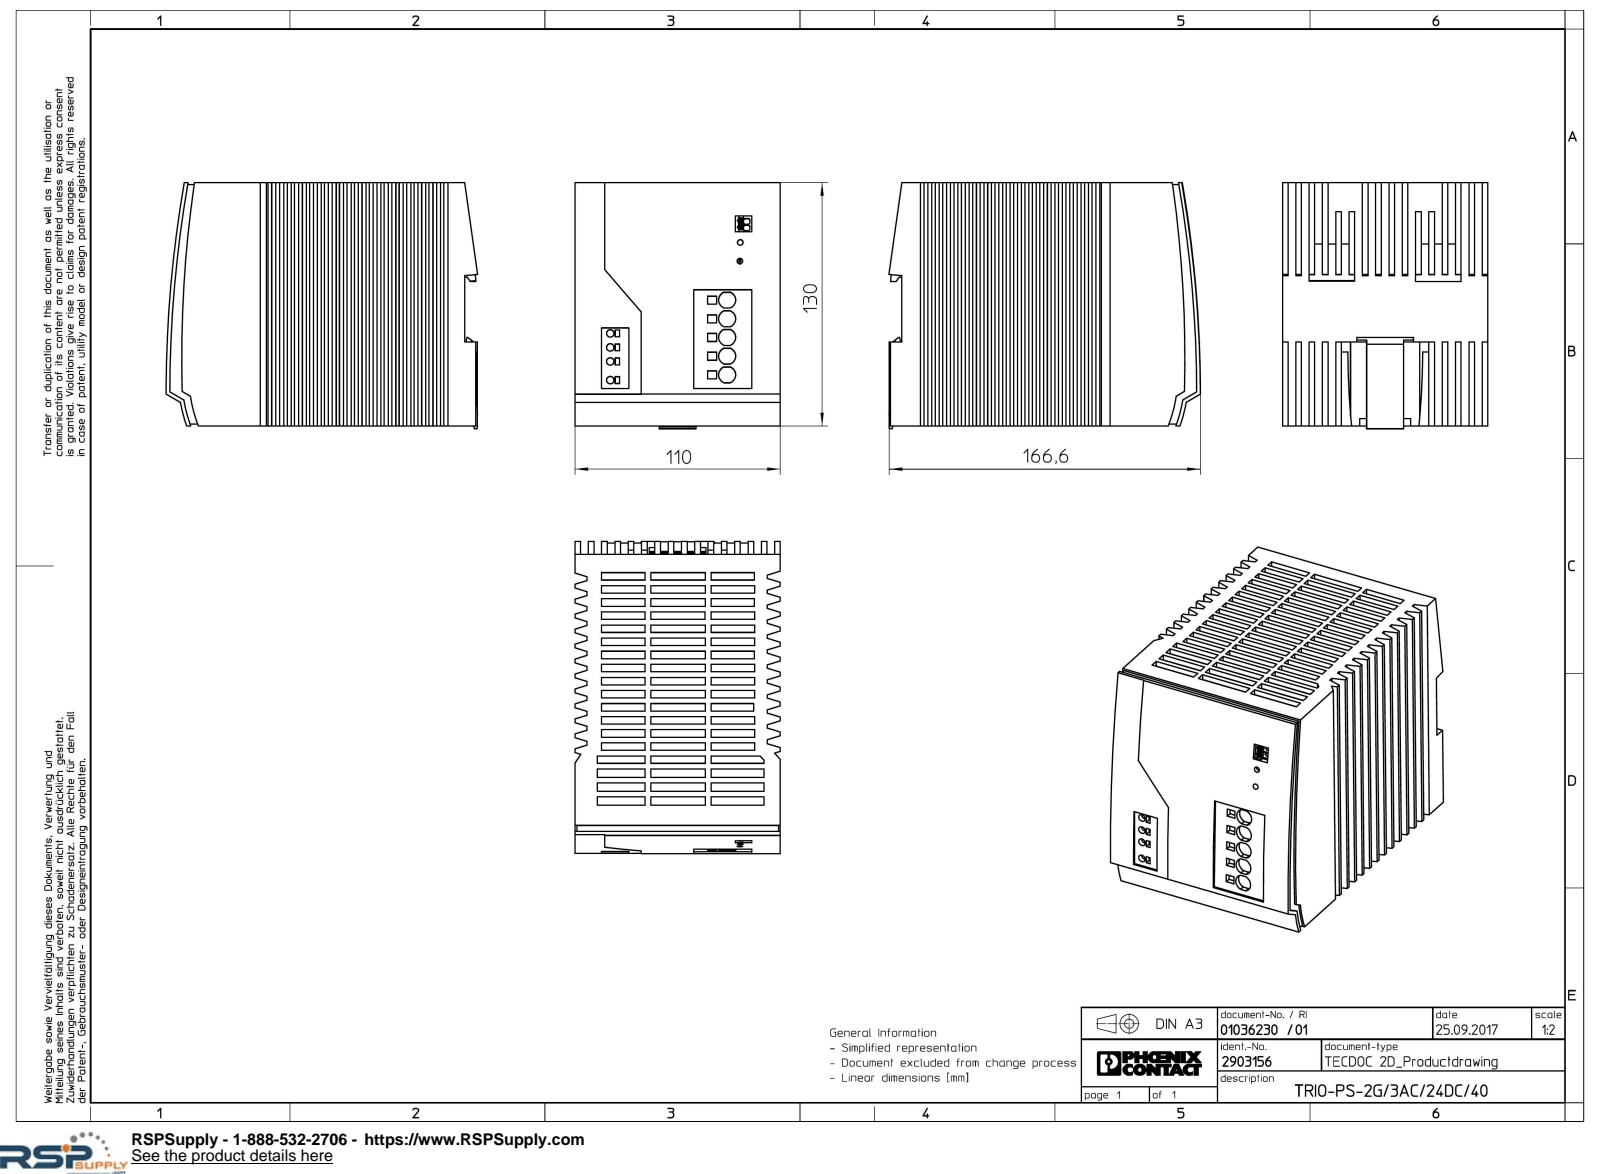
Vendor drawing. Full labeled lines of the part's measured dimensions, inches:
Part name (STEP PRODUCT): TRIO_PS_2G_3AC_24DC_40-select
STEP written by: Creo Elements/Direct Modeling 18.1I 14-Aug-2016 (C) Parametric Technology GmbH (AUTOMOTIVE_DESIGN)
Units: inches
Bodies: 1 solid, 1003 faces (952 planar, 39 cylindrical, 12 other)
Overall size (bounding box): 6.571 × 5.179 × 4.331
Volume: 130.4 in³ · Surface area: 260.1 in²
Round holes (diameter × count): ⌀0.118 ×2
Partial cylindrical surfaces — rounded edges, fillets, slot ends (radius × count): R0.181 ×5, R0.022 ×2, R0.024 ×2, R0.041 ×2, R0.041 ×2, R0.067 ×2, R16.992 ×2, R1.575 ×1
Main face-to-face distances: 0.301, 1.506, 1.204, 0.602, 0.118, 0.903, 0.602, 5, 1.807, 4.331
